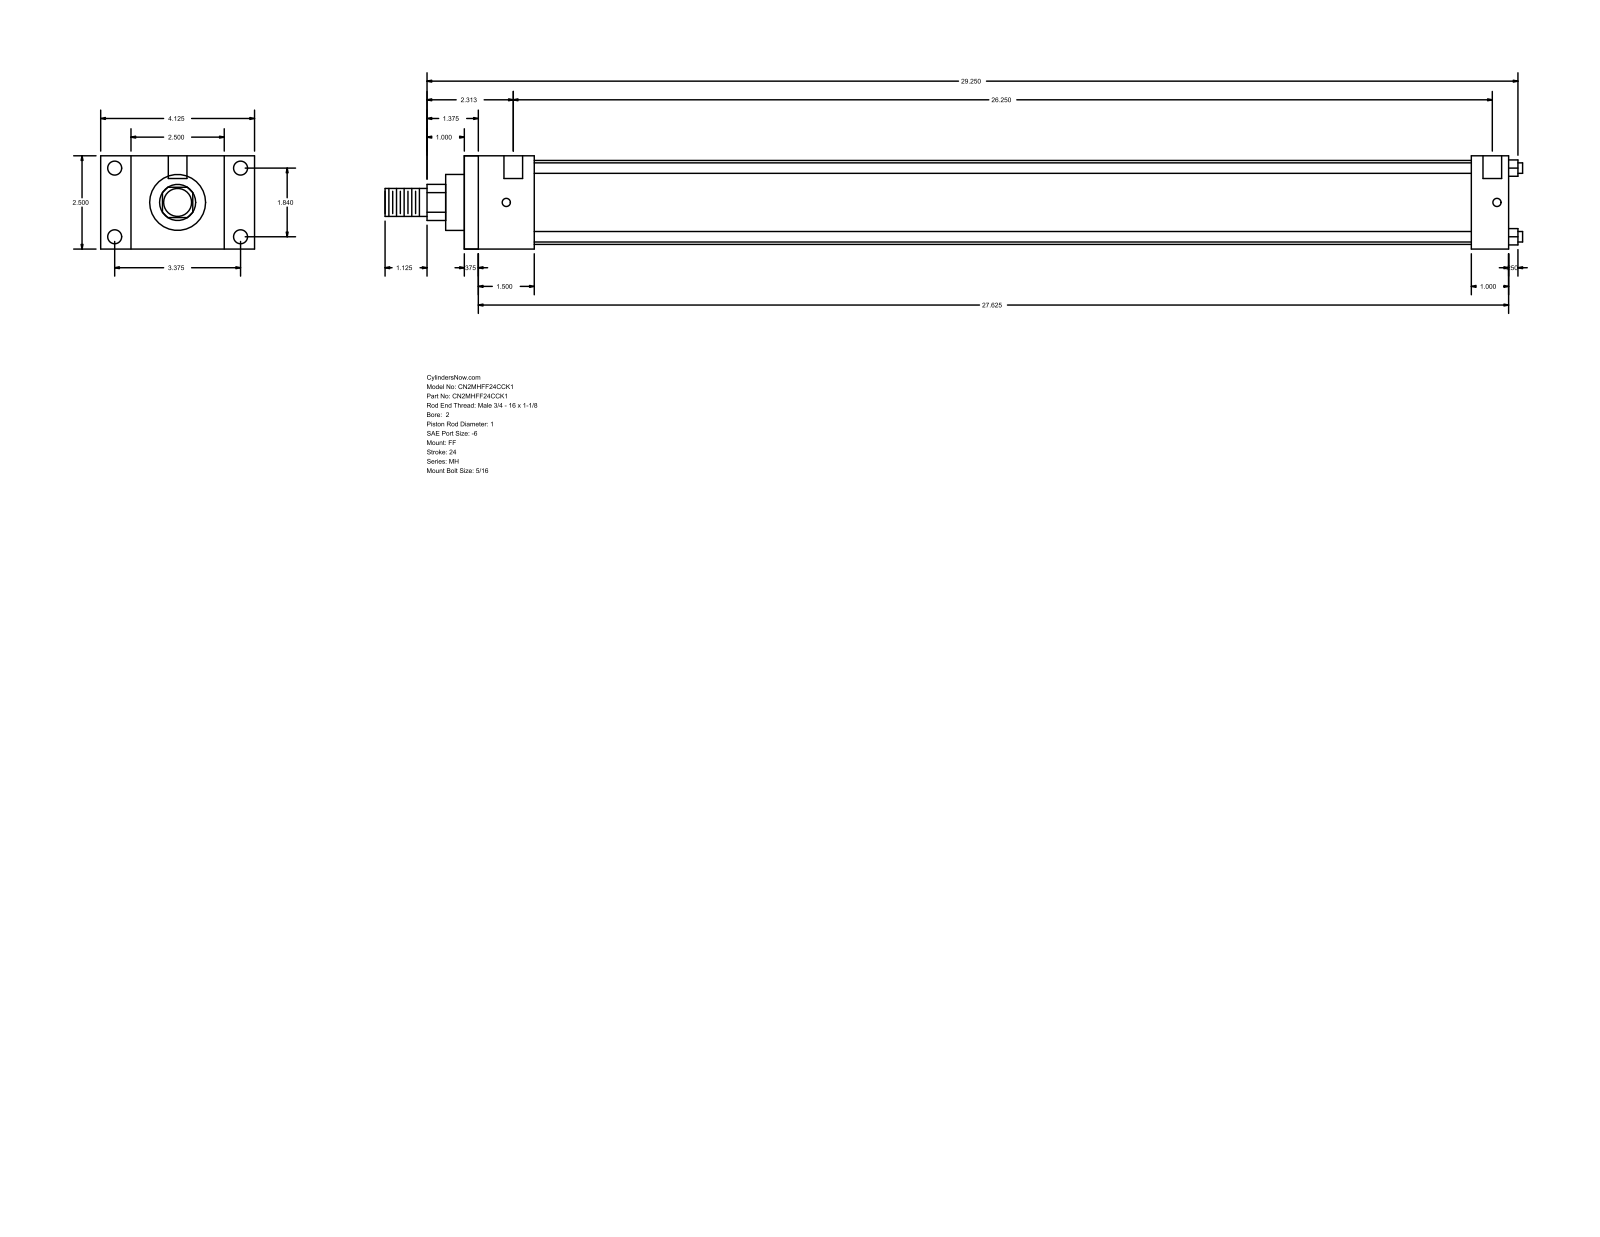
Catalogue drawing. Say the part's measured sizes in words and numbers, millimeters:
The part is named "MH_FF__0200_1". Its 3-D file was written by "GSSL Pune (CONFIG_CONTROL_DESIGN)". It is 0 solids with 92 faces: 64 planar, 28 cylindrical and 0 other. Overall it measures 774.7 by 104.78 by 63.5 millimeters. Round holes: 4 of diameter 5.56, 4 of diameter 9.53, 2 of diameter 12.7. Round bosses or shafts: 4 of diameter 7.14, 1 of diameter 57.15, 1 of diameter 38.1, 1 of diameter 25.4, 1 of diameter 19.05. Partial cylindrical surfaces (rounded edges, fillets, slot ends): 1 of radius 12.29. The main face-to-face distances are 63.5, 711.2, 9.52, 701.68, 20.64, 25.4, 47.63, 685.8, 38.11, 676.28. The hole center spacings are 46.74, 85.72, 97.63, 674.68, 3.17, 4.76, 666.75, 669.92.
